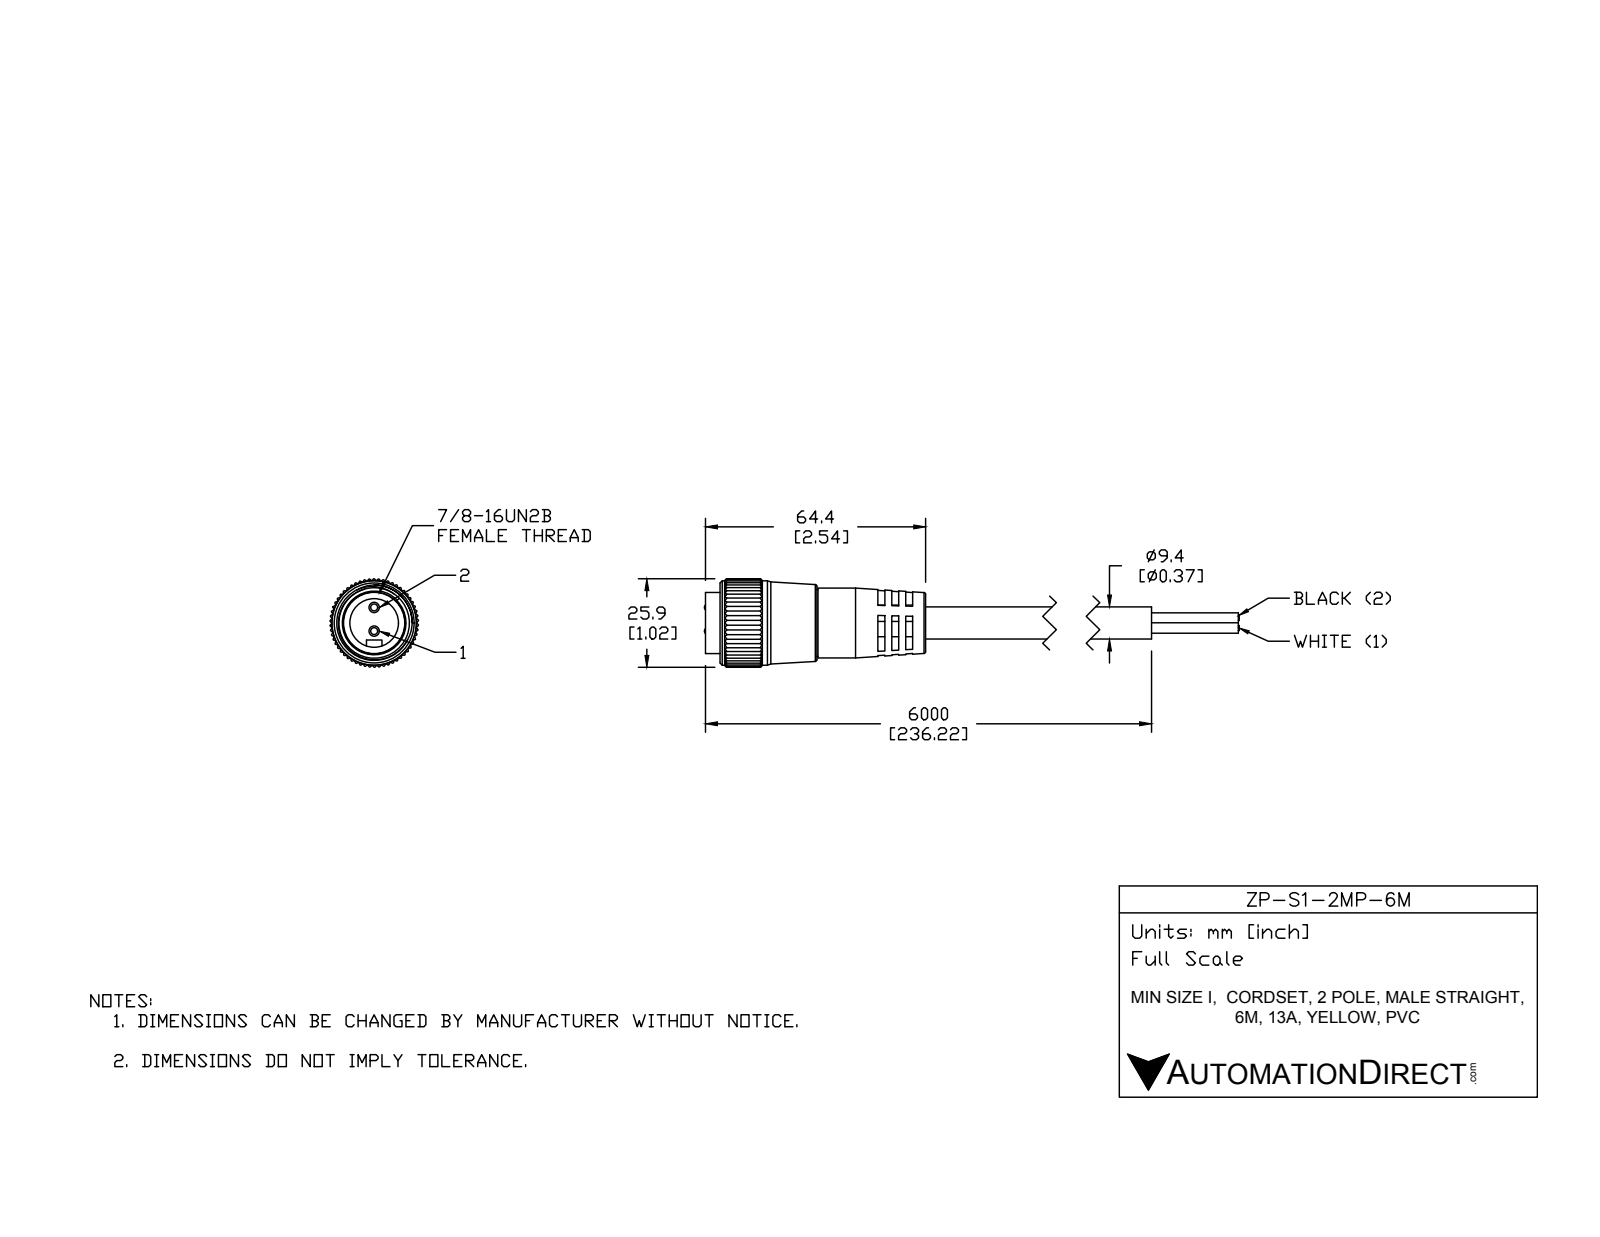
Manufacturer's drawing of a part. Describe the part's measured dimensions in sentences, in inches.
The part is named "ZP-S1-2MP-6M". Its 3-D file was written by "SolidWorks 2015 (AUTOMOTIVE_DESIGN)". It is 4 solids with 516 faces: 176 planar, 310 cylindrical and 30 other. Overall it measures 4.306 by 2.083 by 1.017 inches. Its volume is 1.613 cubic inches and its surface area 19.29 square inches. Round holes: 1 of diameter 0.56, 1 of diameter 0.786, 1 of diameter 0.805, 1 of diameter 0.827. Round bosses or shafts: 2 of diameter 0.37, 2 of diameter 0.12, 2 of diameter 0.079, 1 of diameter 0.972, 1 of diameter 0.803, 1 of diameter 0.768, 1 of diameter 0.704. Partial cylindrical surfaces (rounded edges, fillets, slot ends): 165 of radius 0.01, 1 of radius 0.09, 1 of radius 0.207, 1 of radius 0.509. The main face-to-face distances are 0.079, 0.159, 0.546, 0.468, 0.08, 0.387, 0.238, 0.309, 1.714, 1.793.
